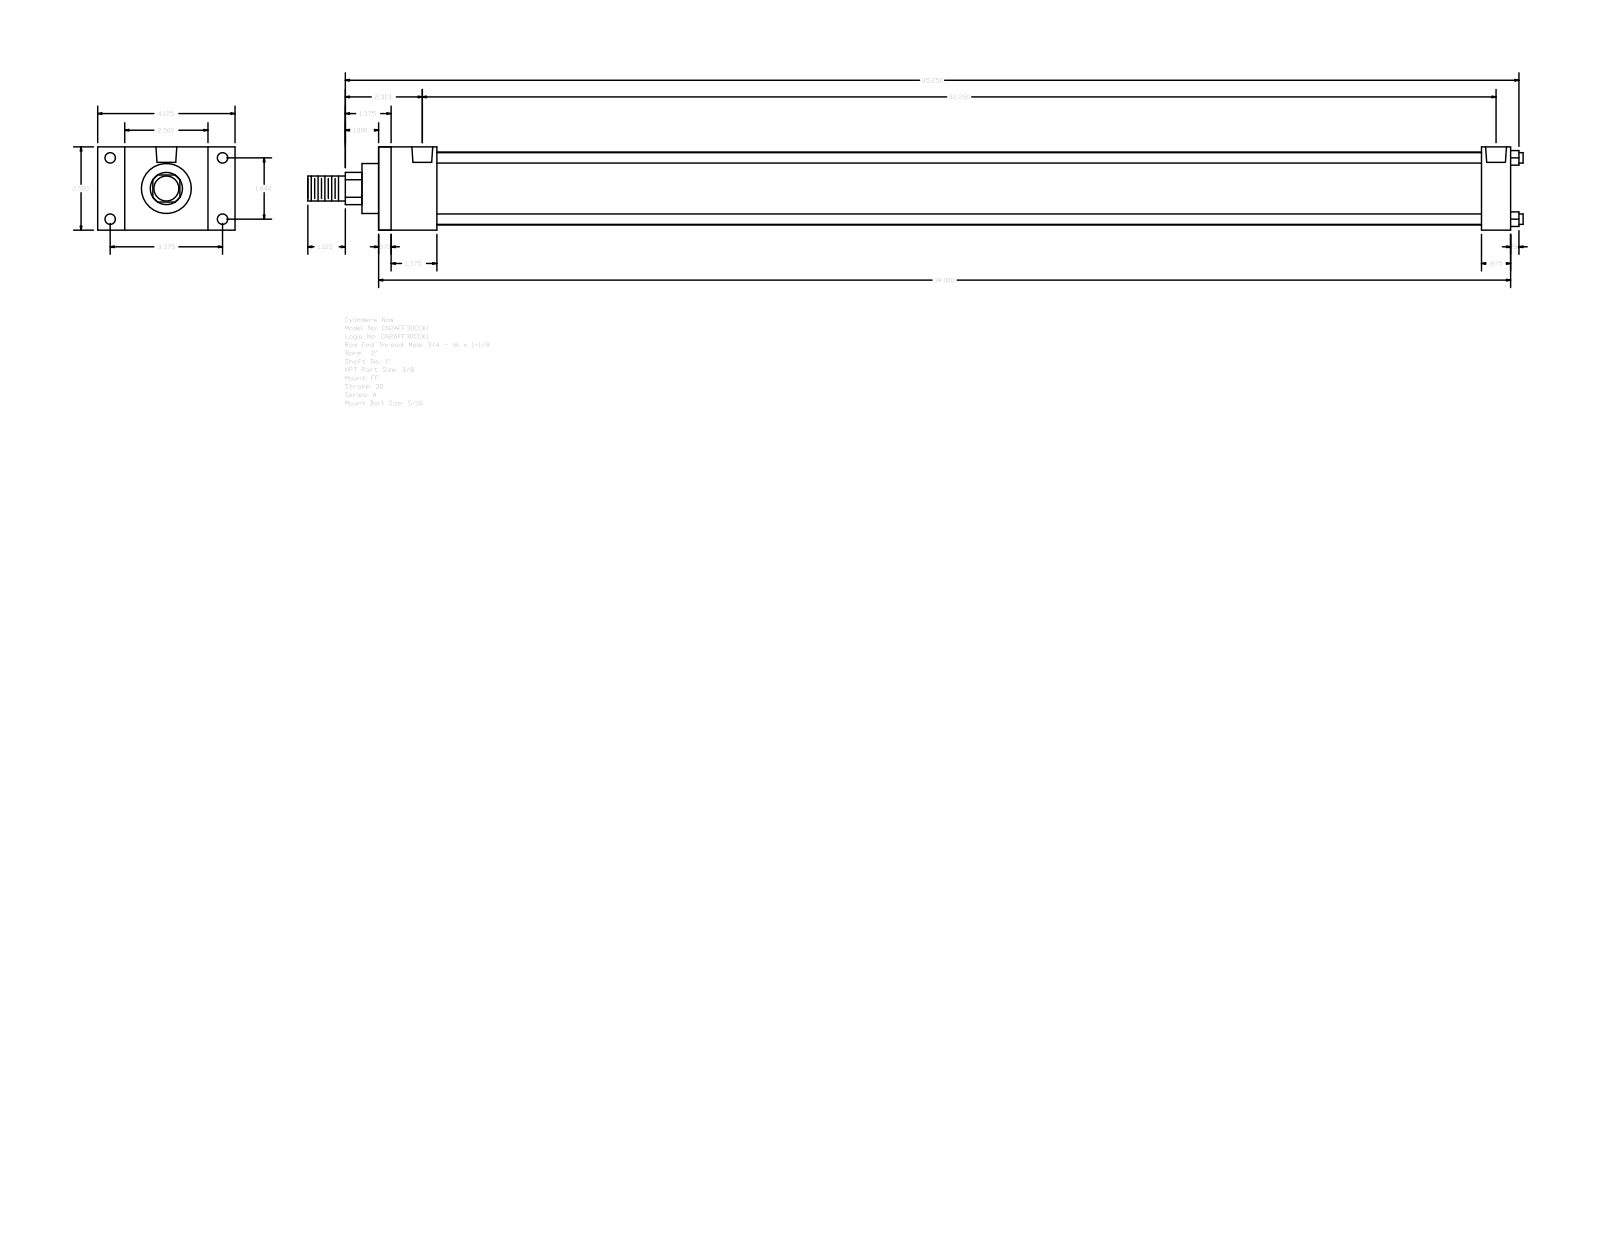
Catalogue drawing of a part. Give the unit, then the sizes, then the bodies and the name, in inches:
Units: inches
Overall size (bounding box): 36.5 × 4.125 × 2.5
Round holes (diameter × count): ⌀0.219 ×4, ⌀0.313 ×4, ⌀0.627 ×2
Round bosses / shafts (diameter × count): ⌀0.313 ×4, ⌀2.19 ×1, ⌀1.5 ×1, ⌀1 ×1, ⌀0.75 ×1
Partial cylindrical surfaces — rounded edges, fillets, slot ends (radius × count): R0.484 ×1
Main face-to-face distances: 2.5, 34, 0.375, 33.625, 0.813, 1.75, 33.125, 1.375, 32.75, 31.375
Hole centre spacings: 1.84, 3.375, 3.844, 32.031, 0.063, 0.157, 32.093, 32.187
Bodies: 0 solids, 92 faces (64 planar, 28 cylindrical, 0 other)
Part name (STEP PRODUCT): A_FF__0200_1
STEP written by: GSSL Pune (CONFIG_CONTROL_DESIGN)
